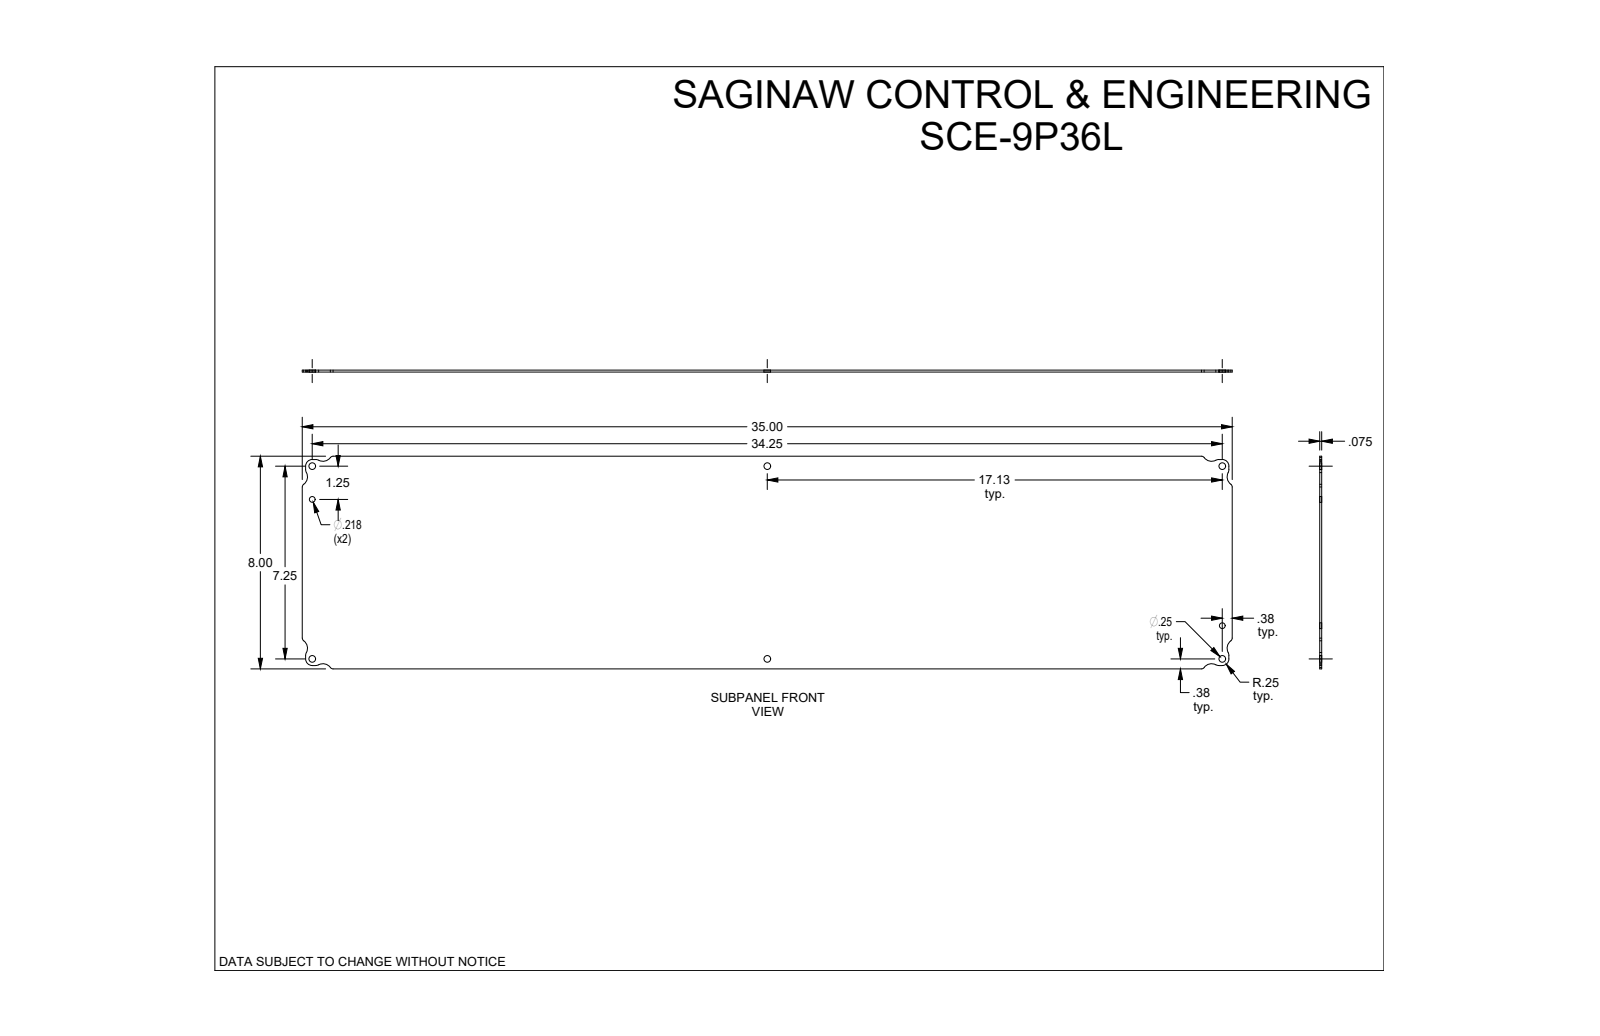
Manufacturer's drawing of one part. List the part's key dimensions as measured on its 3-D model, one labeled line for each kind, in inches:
Part name (STEP PRODUCT): SCE-9P36L
STEP written by: SolidWorks 2019 (CONFIG_CONTROL_DESIGN)
Units: inches
Bodies: 1 solid, 50 faces (14 planar, 36 cylindrical, 0 other)
Overall size (bounding box): 35 × 8 × 0.075
Volume: 20.88 in³ · Surface area: 563.7 in²
Round holes (diameter × count): ⌀0.25 ×6, ⌀0.218 ×2
Partial cylindrical surfaces — rounded edges, fillets, slot ends (radius × count): R0.25 ×12, R0.125 ×8, R0.344 ×8
Main face-to-face distances: 0.075, 8, 35, 0.125, 7.875, 34.875, 7.75, 34.75
Hole centre spacings: 17.125, 18.596, 7.25, 1.25, 6, 17.17, 18.145, 34.25
